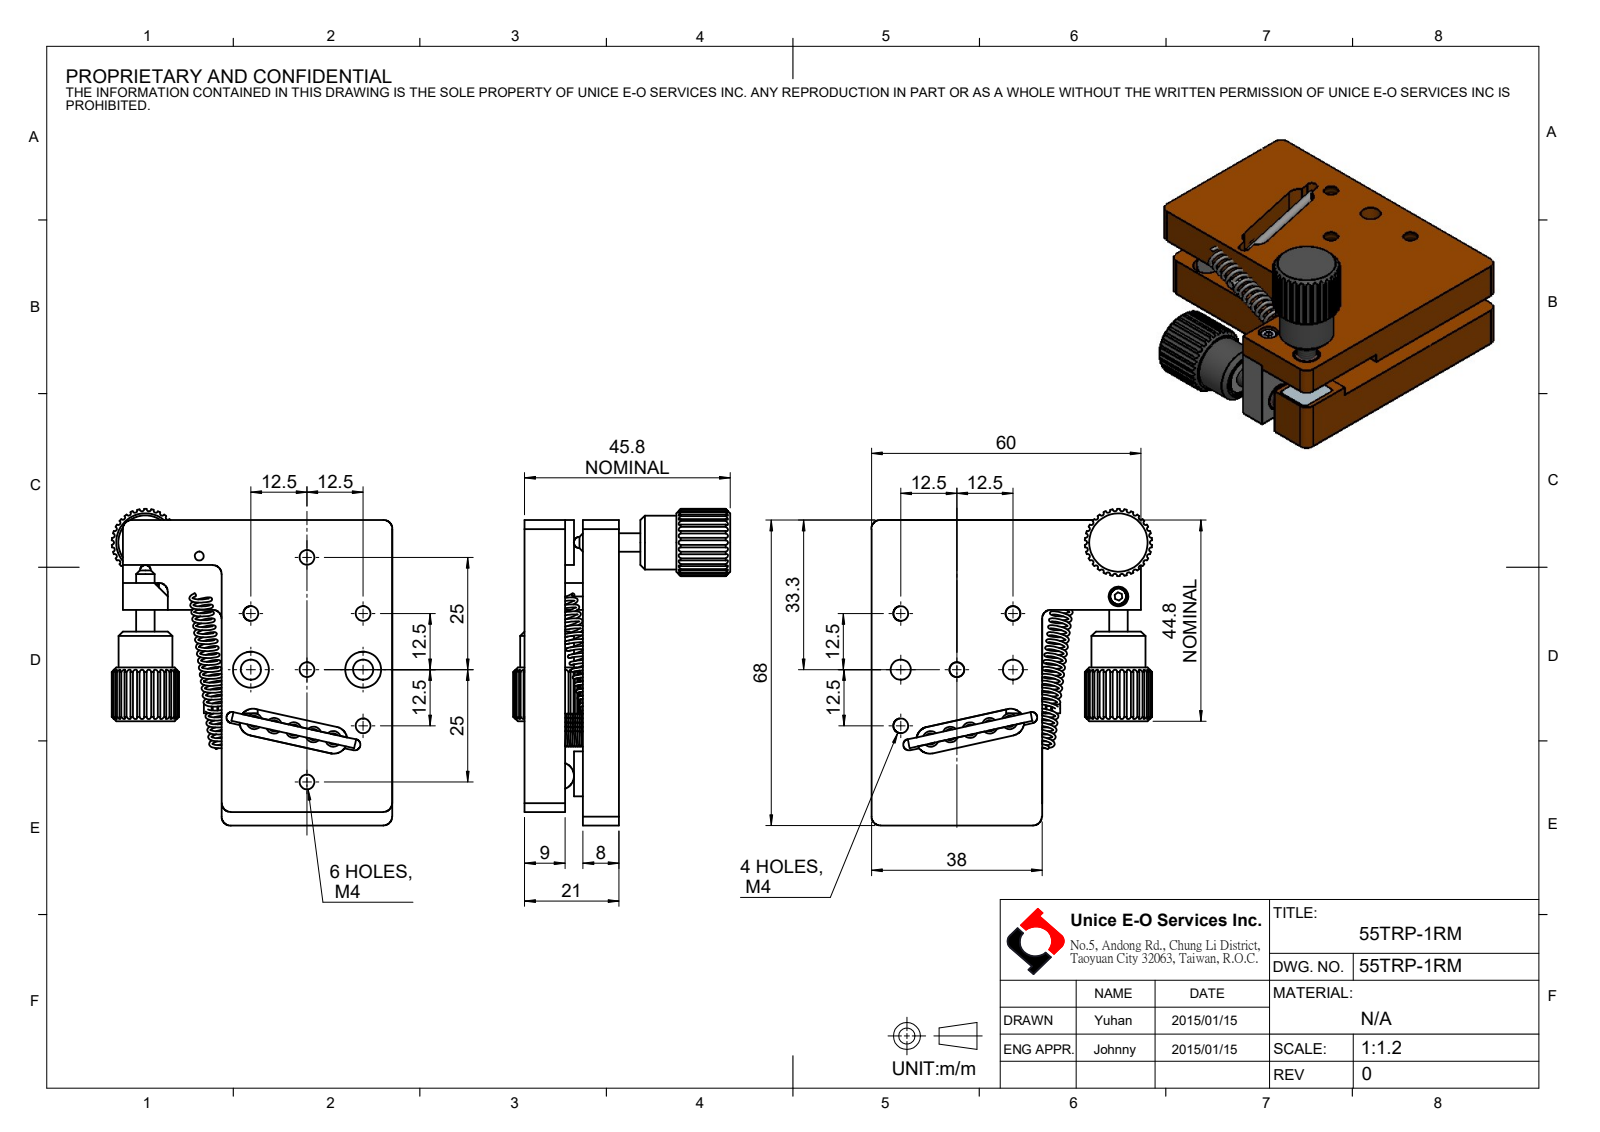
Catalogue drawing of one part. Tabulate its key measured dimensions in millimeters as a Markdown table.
| quantity | value |
| --- | --- |
| part name | 55TRP-1RM |
| STEP written by | SolidWorks 2016 (CONFIG_CONTROL_DESIGN) |
| units | millimeters |
| bodies | 25 solids, 519 faces (136 planar, 304 cylindrical, 79 other) |
| overall size | 70.5 × 62.48 × 48.3 |
| volume | 49 439 mm³ |
| surface area | 26 197 mm² |
| round holes (diameter × count) | 3.3 × 9, 2 × 2, 3.45 × 2, 4.5 × 2, 6 × 2, 8 × 2, 9 × 2, 1.6 × 1, 2.4 × 1, 4.4 × 1, 5 × 1 |
| round bosses / shafts (diameter × count) | 2 × 3, 12 × 2, 6 × 2, 4.1 × 2, 3.8 × 1, 2.5 × 1, 1.2 × 1 |
| partial cylindrical surfaces (radius × count) | 0.5 × 60, 2 × 9, 0.75 × 8, 1 × 8, 3 × 6, 1.25 × 2, 7.5 × 2 |
| main face-to-face distances | 12, 8, 4, 21, 9, 13, 6, 2, 38, 10 |
| hole center spacings | 27.95, 17.68, 12.5, 25, 39.53, 12.37, 14, 3 |
